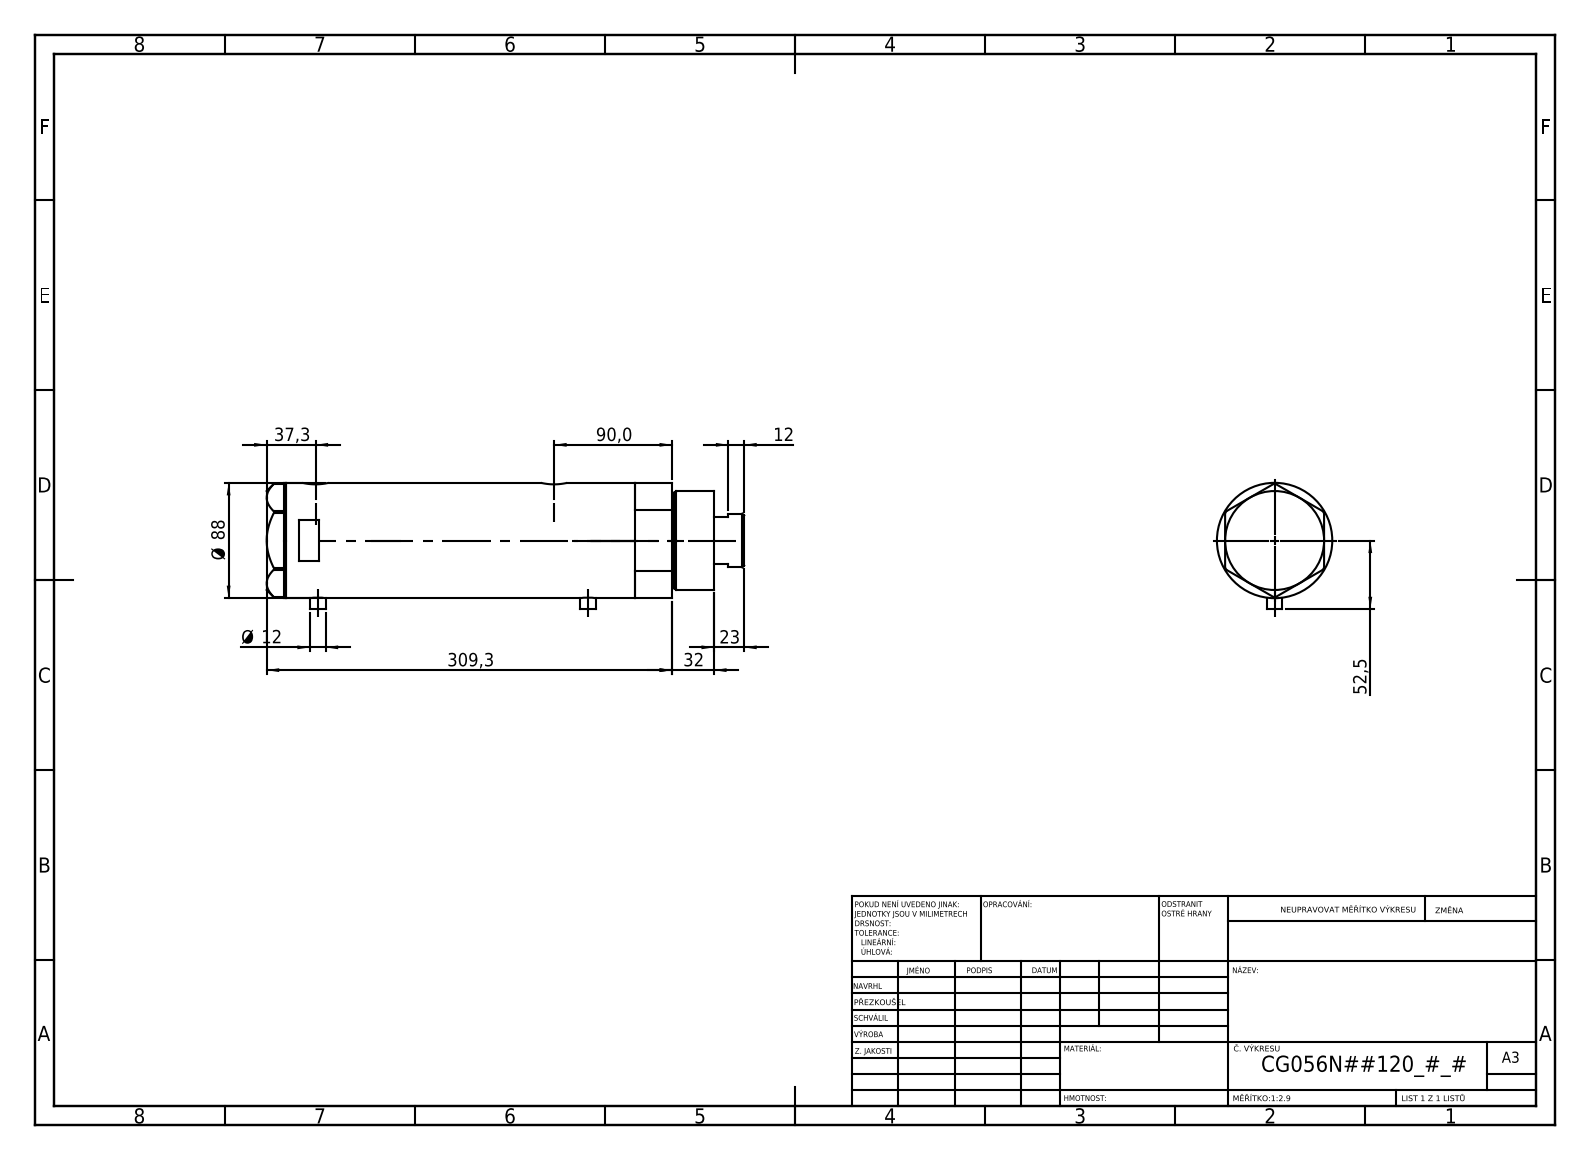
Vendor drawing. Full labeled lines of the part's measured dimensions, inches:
Part name (STEP PRODUCT): V270CG_VC; V270CG_BACK; V270CG_MIDDLE; V270CG_FRONT
STEP written by: SolidWorks 2019 (CONFIG_CONTROL_DESIGN)
Units: inches
Bodies: 4 solids, 121 faces (52 planar, 49 cylindrical, 20 other)
Overall size (bounding box): 14.343 × 3.799 × 3.465
Volume: 115 in³ · Surface area: 406.6 in²
Round holes (diameter × count): ⌀0.492 ×2, ⌀0.518 ×2, ⌀0.787 ×2, ⌀0.571 ×1, ⌀1.654 ×1, ⌀1.713 ×1, ⌀2.205 ×1, ⌀2.362 ×1, ⌀3.15 ×1
Round bosses / shafts (diameter × count): ⌀0.472 ×2, ⌀3.465 ×1, ⌀2.953 ×1, ⌀2.874 ×1, ⌀1.614 ×1
Main face-to-face distances: 8.047, 1.024, 7.024, 0.591, 1.614, 8.638, 12.846, 13.437, 11.823, 4.799
Hole centre spacings: 0.067, 1.016, 7.098, 7.165, 8.114, 8.181
